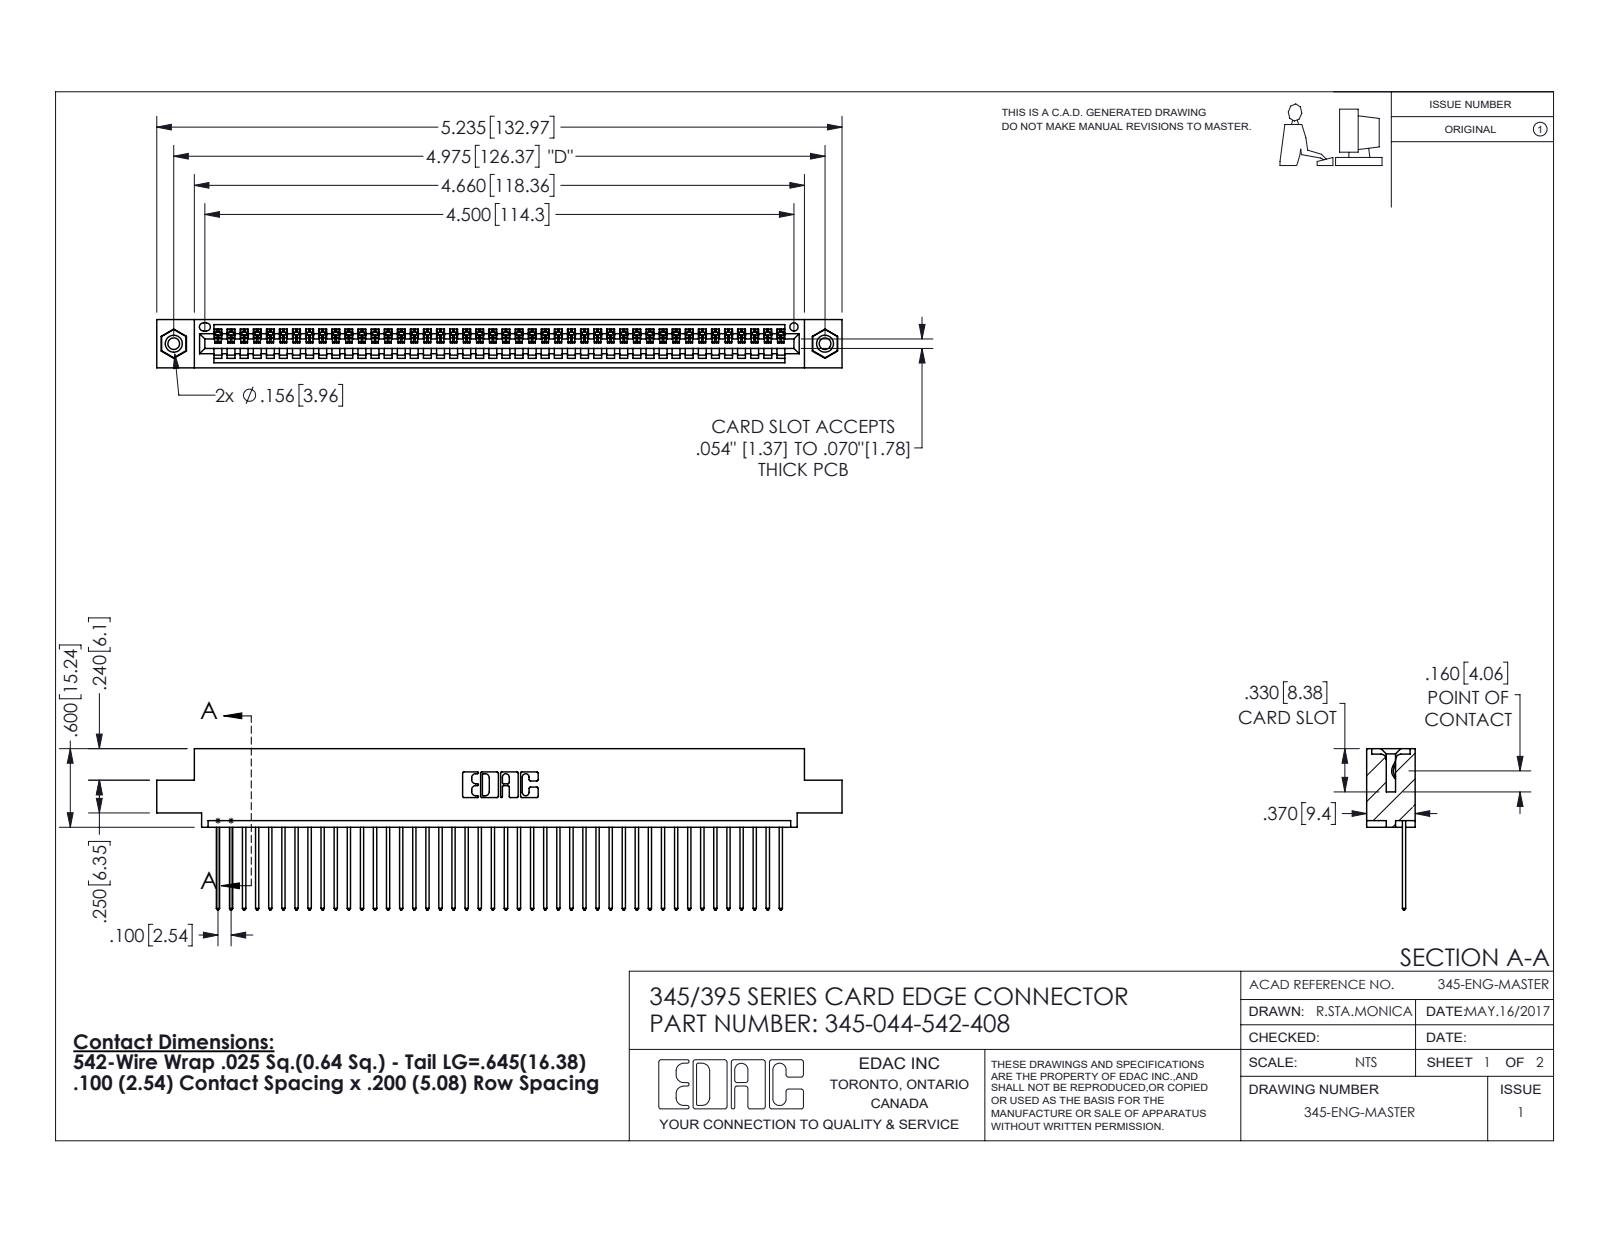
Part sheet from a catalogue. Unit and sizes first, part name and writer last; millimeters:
Units: millimetres
Overall size (bounding box): 133 × 31.3 × 9.4
Round holes (diameter × count): ⌀2.3 ×2, ⌀3.2 ×2, ⌀4 ×2, ⌀1.6 ×1
Round bosses / shafts (diameter × count): ⌀3.9 ×2
Partial cylindrical surfaces — rounded edges, fillets, slot ends (radius × count): R0.2 ×88, R0.3 ×88, R0.3 ×22, R0.2 ×6, R0.8 ×6, R0.7 ×3, R0.8 ×2, R1 ×2
Main face-to-face distances: 1.8, 7.6, 9.4, 2.5, 6.9, 0.6, 5.1, 5.7, 3.8, 1.8
Hole centre spacings: 6.9, 120.4, 126.4
Volume: 12 700 mm³ · Surface area: 17 570 mm²
Bodies: 47 solids, 2742 faces (1876 planar, 850 cylindrical, 16 other)
Part name (STEP PRODUCT): 345-292-001_345-293-142; 345-250-001_345-250-003-102; 345 Part_0.110 Offset - 0.156 Dia-TI; 345-044-542-408
STEP written by: SolidWorks 2016 (CONFIG_CONTROL_DESIGN)
